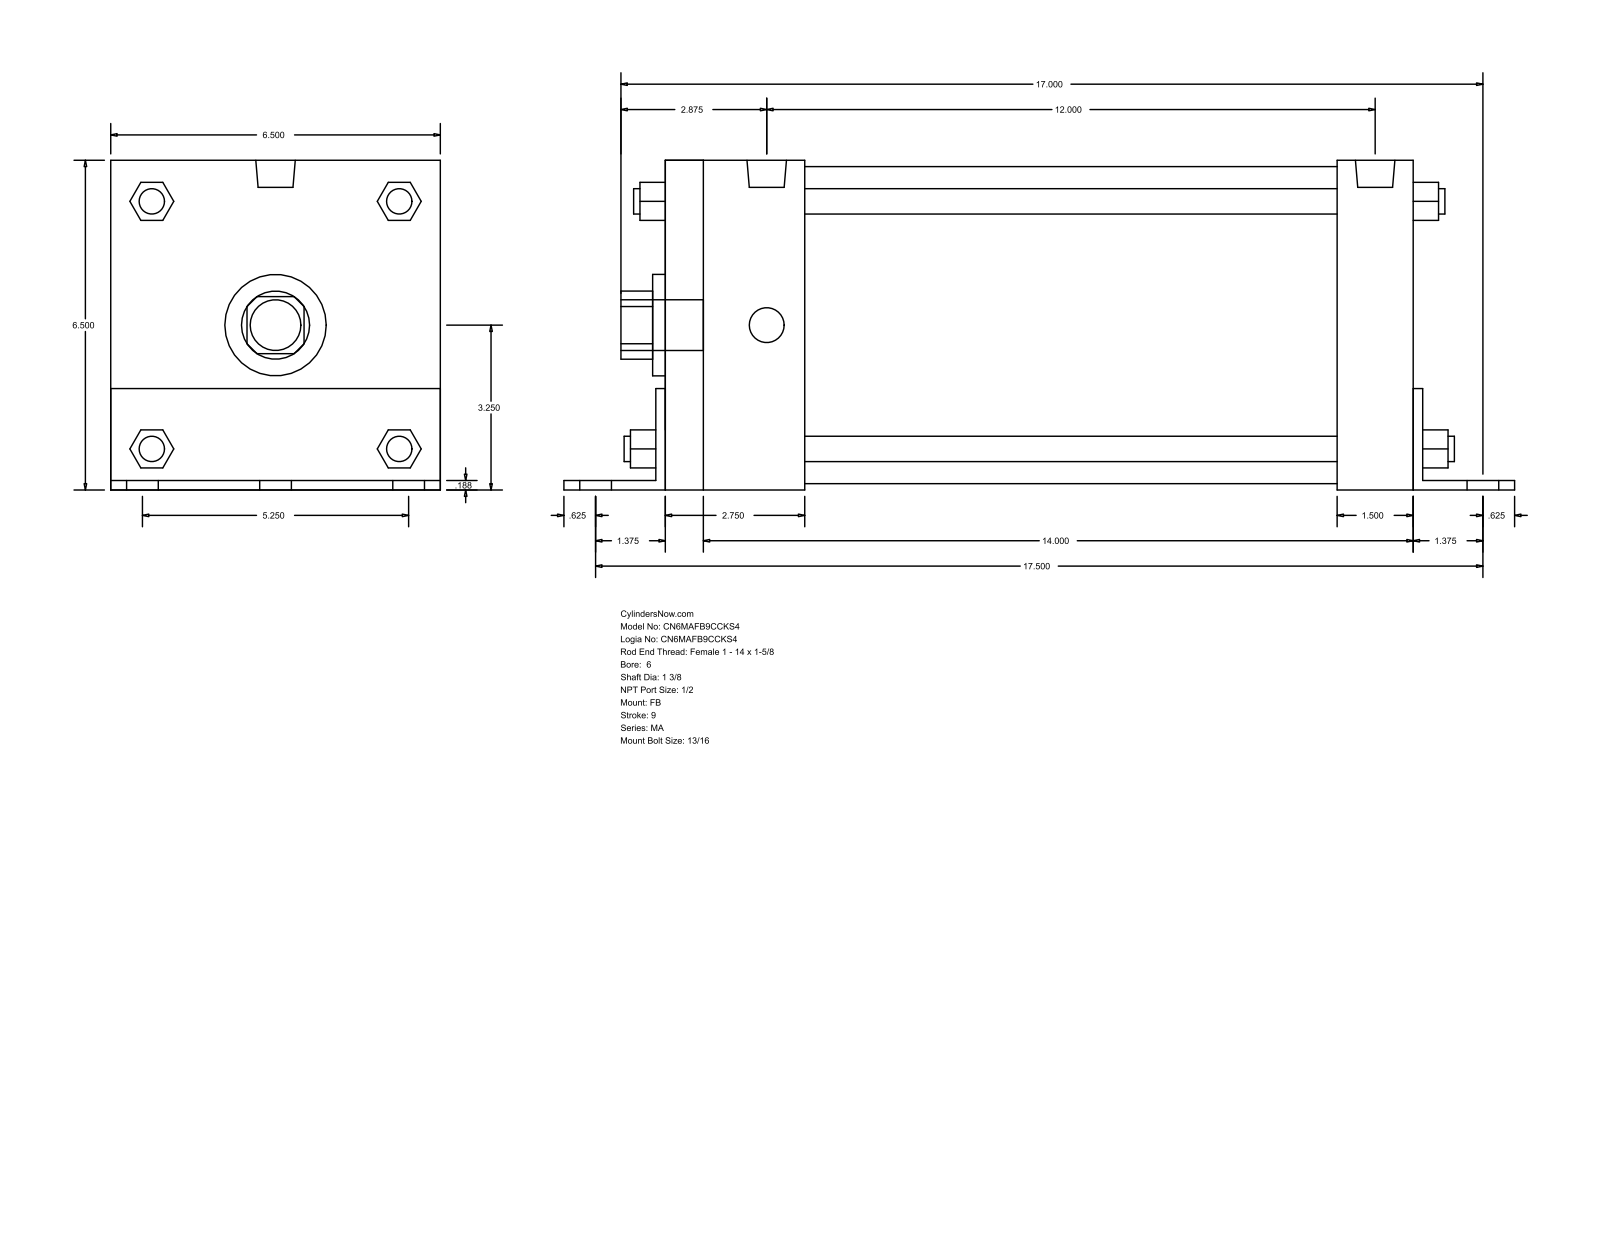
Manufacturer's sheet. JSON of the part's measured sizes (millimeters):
{"part_name": "MA_FB__0600_1.375", "step_written_by": "GSSL Pune (CONFIG_CONTROL_DESIGN)", "units": "millimeters", "bodies": {"solids": 0, "faces": 140, "planar": 105, "cylindrical": 35, "other": 0}, "overall_size": [473.07, 165.15, 165.1], "round_holes": [[34.92, 1], [50.8, 1], [158.75, 1]], "round_bosses_or_shafts": [[20.64, 6], [17.46, 4], [12.7, 4], [19.77, 2], [25.4, 1]], "partial_cylinders_radius": [[17.06, 1], [32.05, 1]], "face_to_face_distances": [165.1, 4.76, 371.47, 165.15, 4.71, 160.39, 4.77, 38.1, 376.24, 381]}
